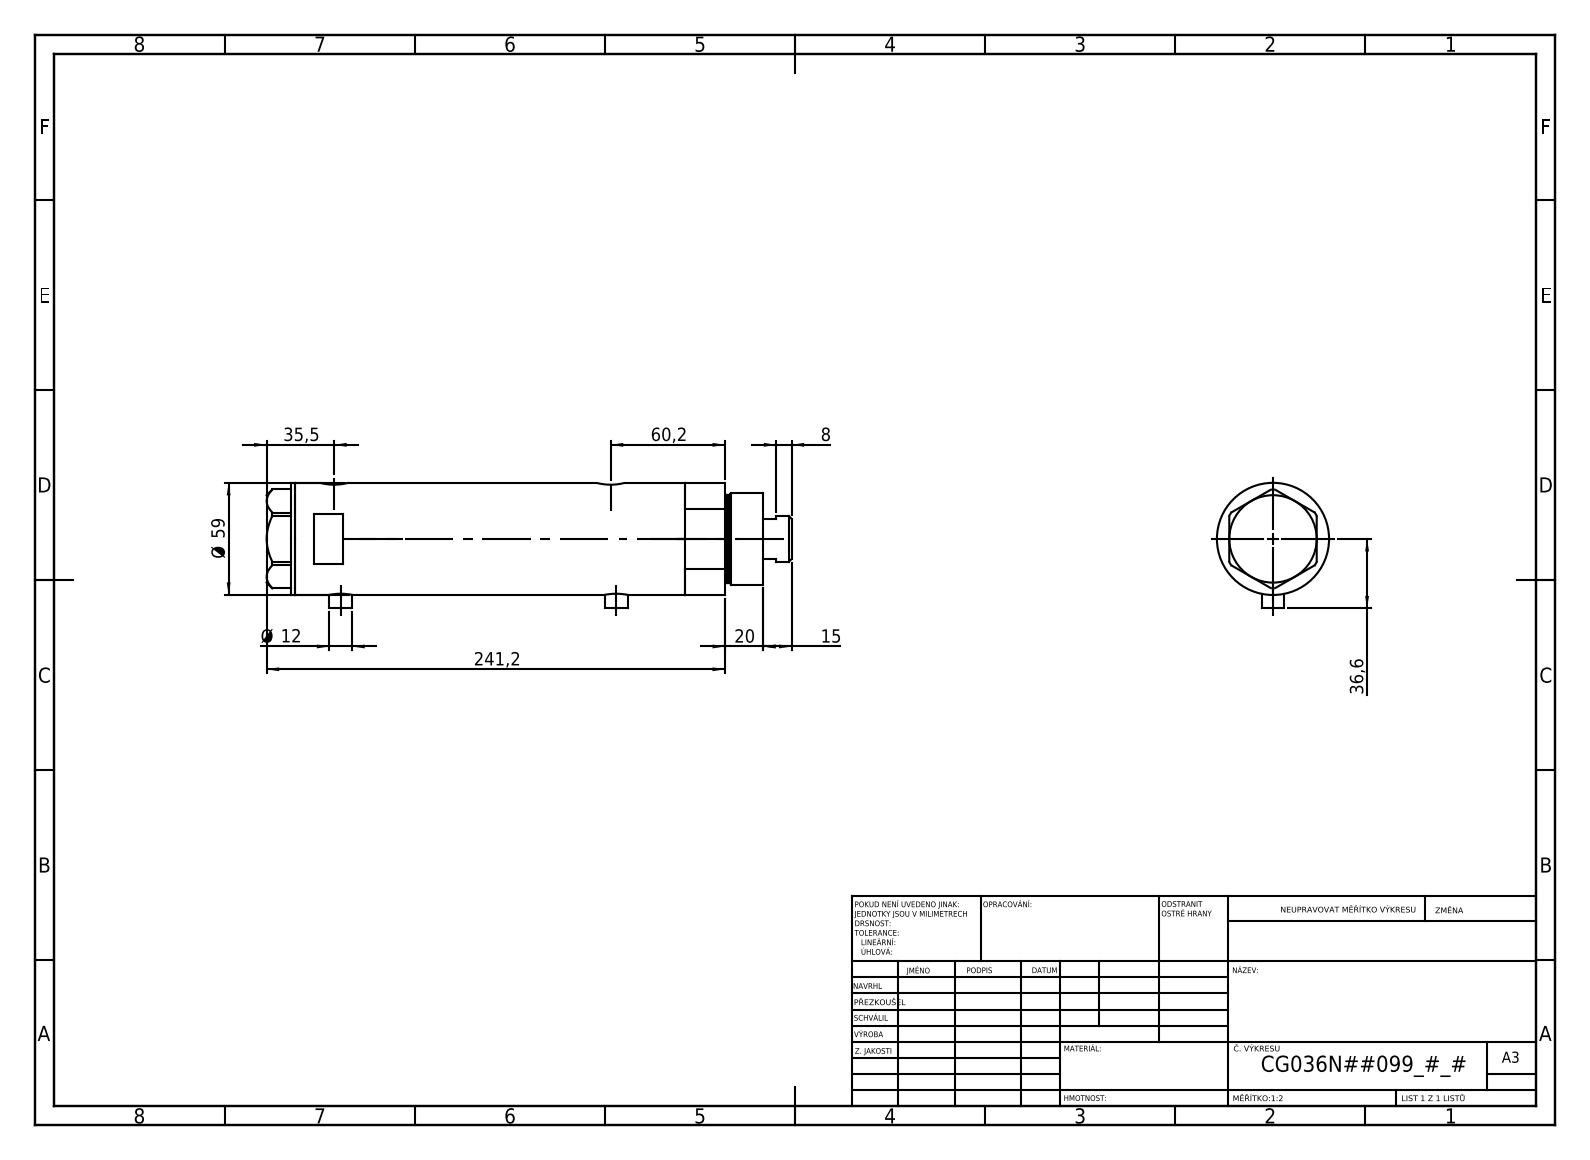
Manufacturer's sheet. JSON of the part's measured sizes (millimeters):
{"part_name": "V270CG_FRONT; V270CG_VC; V270CG_BACK; V270CG_MIDDLE", "step_written_by": "SolidWorks 2019 (CONFIG_CONTROL_DESIGN)", "units": "millimeters", "bodies": {"solids": 4, "faces": 120, "planar": 51, "cylindrical": 49, "other": 20}, "overall_size": [276.2, 66.1, 59], "volume_mm3": 630329, "surface_area_mm2": 125032, "round_holes": [[9.73, 2], [12.5, 2], [15, 2], [8.5, 1], [25, 1], [26.5, 1], [36, 1], [40, 1], [52, 1]], "round_bosses_or_shafts": [[12, 2], [59, 1], [48, 1], [46, 1], [24, 1]], "face_to_face_distances": [167.2, 23.5, 143.7, 15, 38.5, 182.2, 2, 261.2, 246.2, 222.7], "hole_center_spacings": [2.9, 3.5, 142, 144.9, 145.5, 148.4]}
